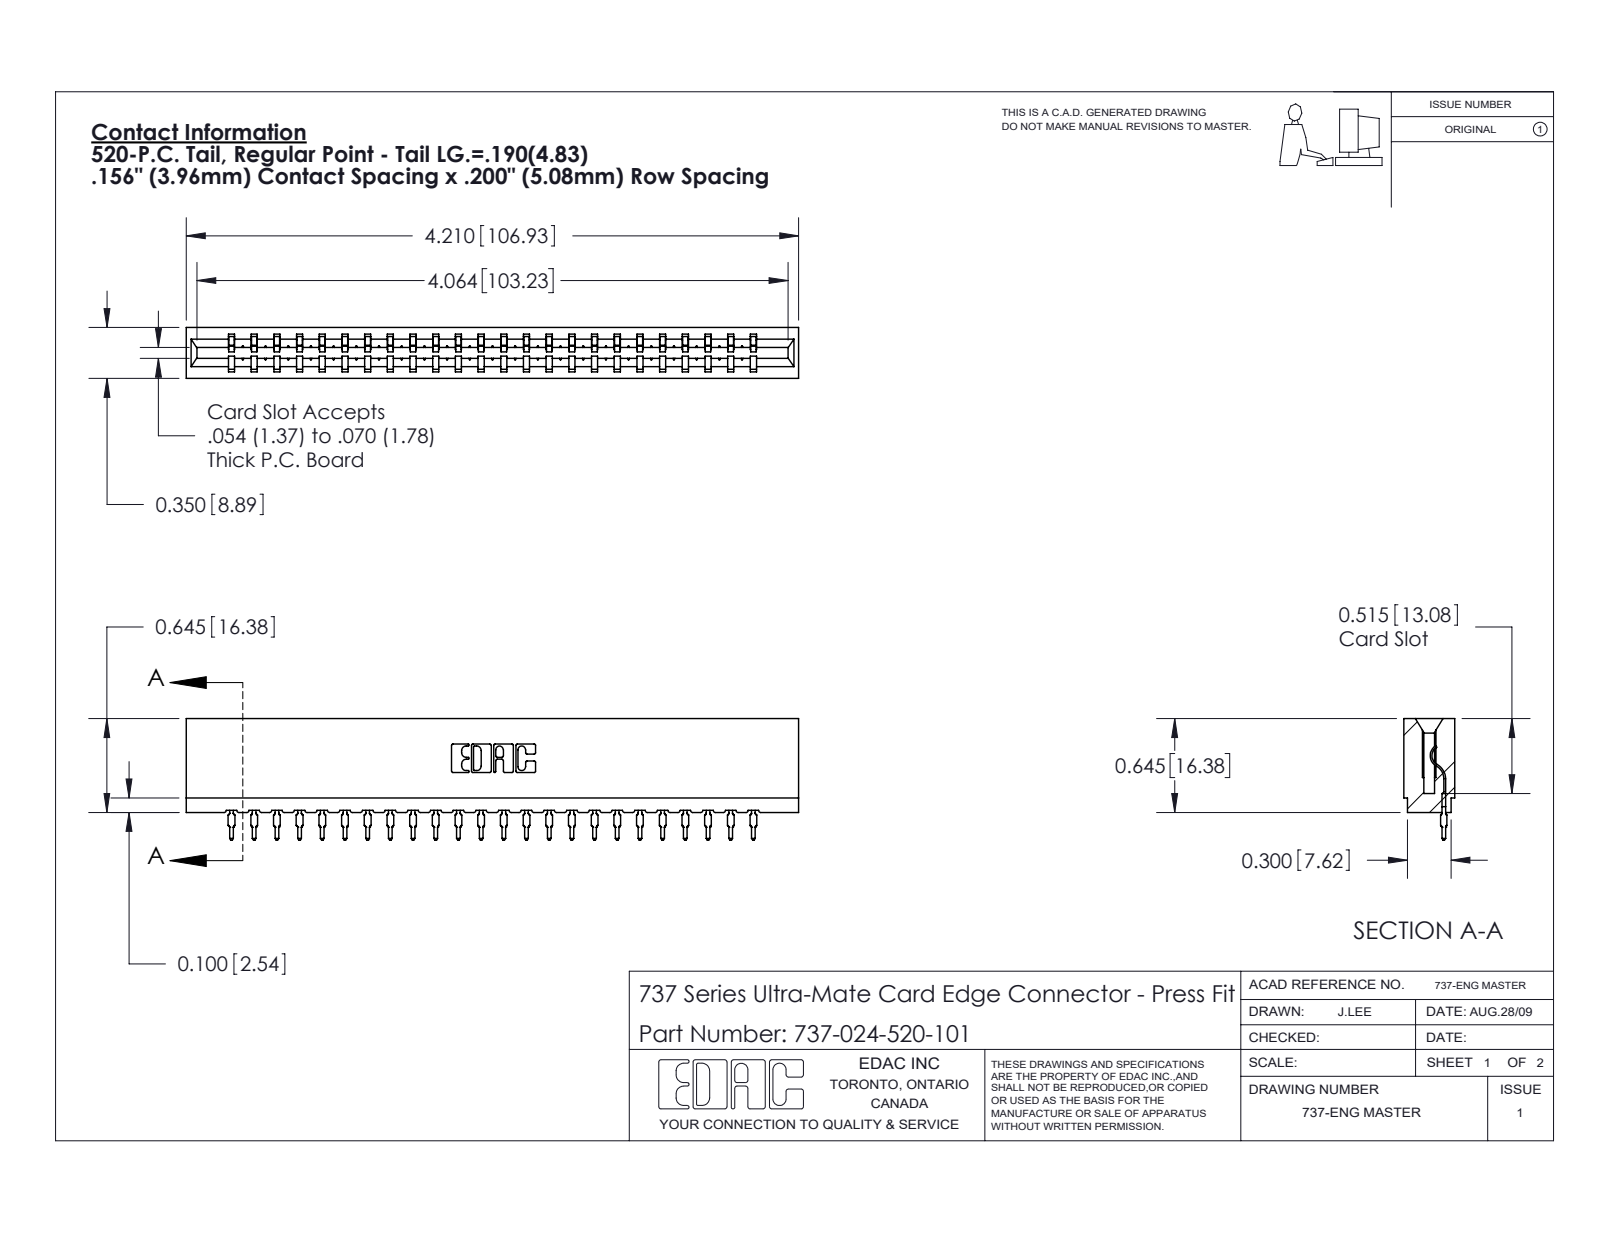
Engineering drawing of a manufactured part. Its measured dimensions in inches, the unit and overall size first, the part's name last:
Units: inches
Overall size (bounding box): 4.21 × 0.836 × 0.35
Partial cylindrical surfaces — rounded edges, fillets, slot ends (radius × count): R0.015 ×48, R0.021 ×48, R0.01 ×22, R0.007 ×6, R0.031 ×6, R0.005 ×4, R0.011 ×4, R0.026 ×3
Main face-to-face distances: 0.138, 0.212, 0.35, 0.074, 0.624, 0.156, 0.045, 0.305, 0.093, 0.167
Volume: 0.636 in³ · Surface area: 20.95 in²
Bodies: 25 solids, 2806 faces (1686 planar, 496 cylindrical, 624 other)
Part name (STEP PRODUCT): 737-024-520-101; 745-292-001_520; 737 Part_Insulator Option - 01
STEP written by: SolidWorks 2020 (CONFIG_CONTROL_DESIGN)
